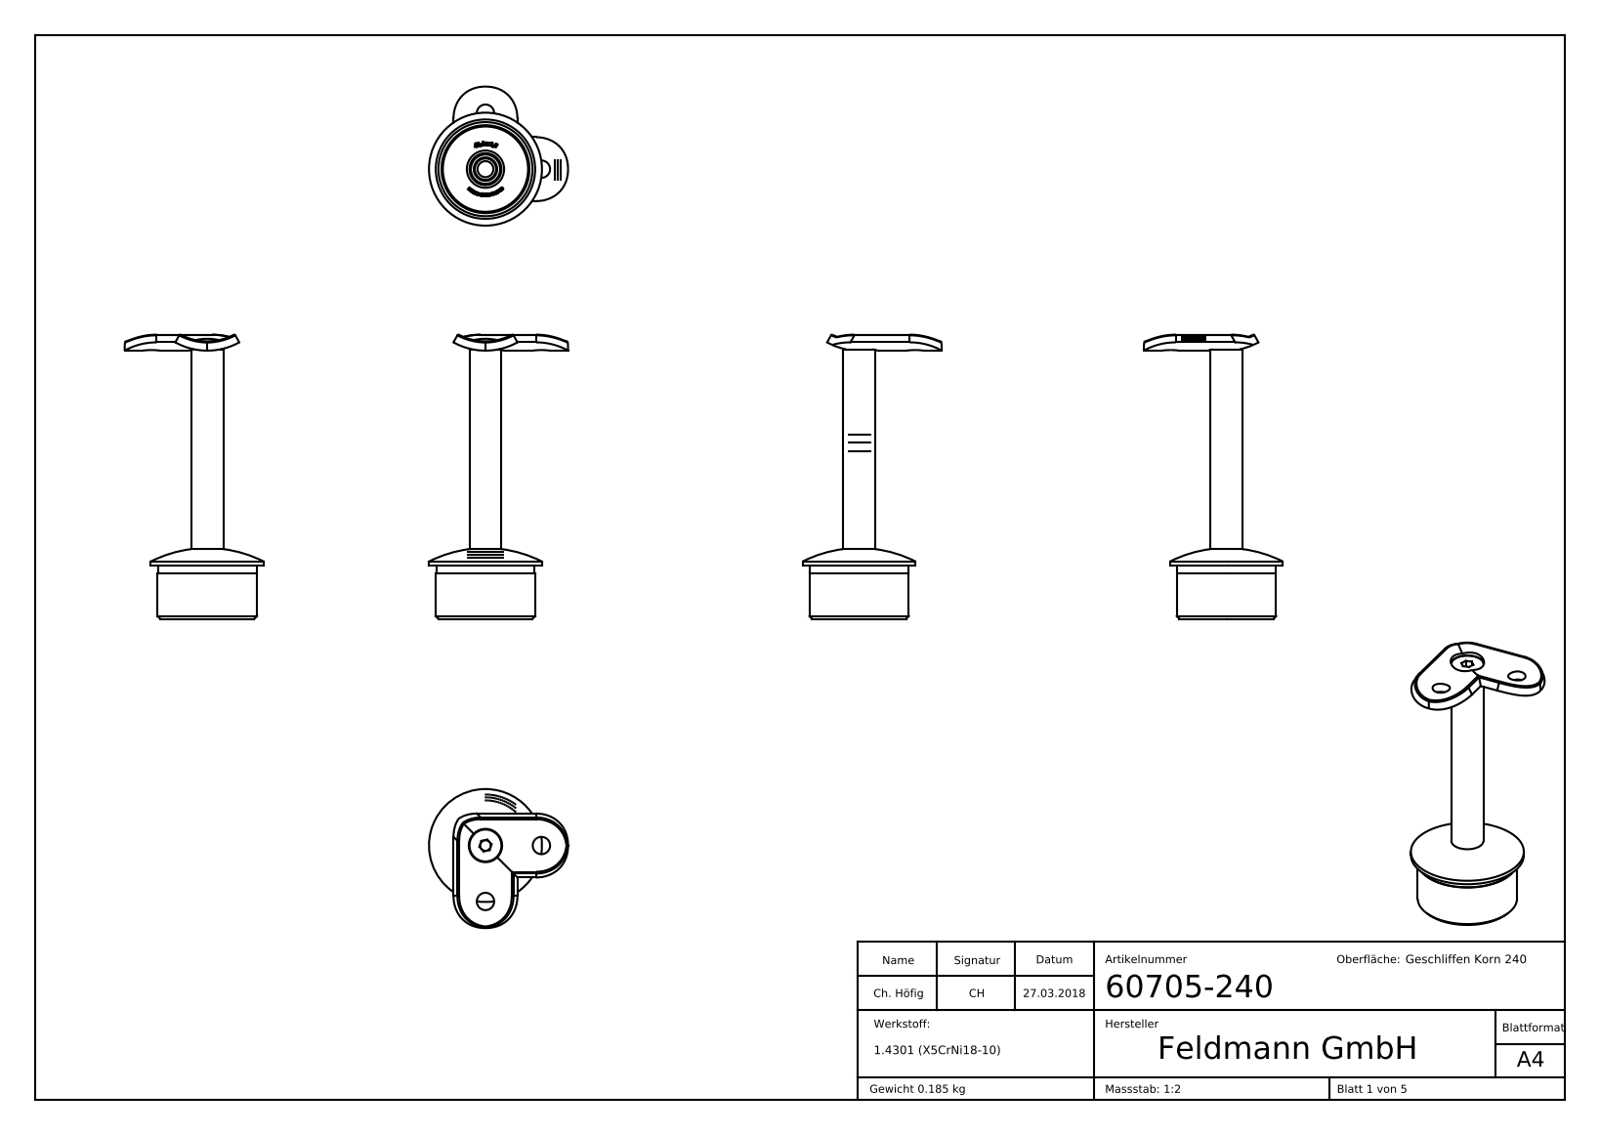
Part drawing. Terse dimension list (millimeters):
name: 6027X-240; 60179-240_60179-240; 60705-240; DIN-7991_-_DIN7991 M6x16 (+5 more)
written by: SolidWorks 2018 (CONFIG_CONTROL_DESIGN)
unit: mm
bodies: 4 solids, 390 faces (222 planar, 31 cylindrical, 137 other)
size: 108.18 × 52.2 × 52.2
volume: 26 525 mm³; area: 15 853 mm²
holes: 2× ⌀6.5, 1× ⌀5, 1× ⌀6.8, 1× ⌀8.5, 1× ⌀12.5, 1× ⌀14, 1× ⌀33
bosses: 1× ⌀42.4, 1× ⌀37.3, 1× ⌀36.9, 1× ⌀12, 1× ⌀8, 1× ⌀6
rounds: 4× R0.5, 4× R12, 2× R21.2, 2× R24.7, 1× R10
face distances: 0.5, 81.03, 80.53, 20, 20.5, 101.03, 83.58, 103.58, 83.08, 2.55
hole spacings: 21, 29.7
